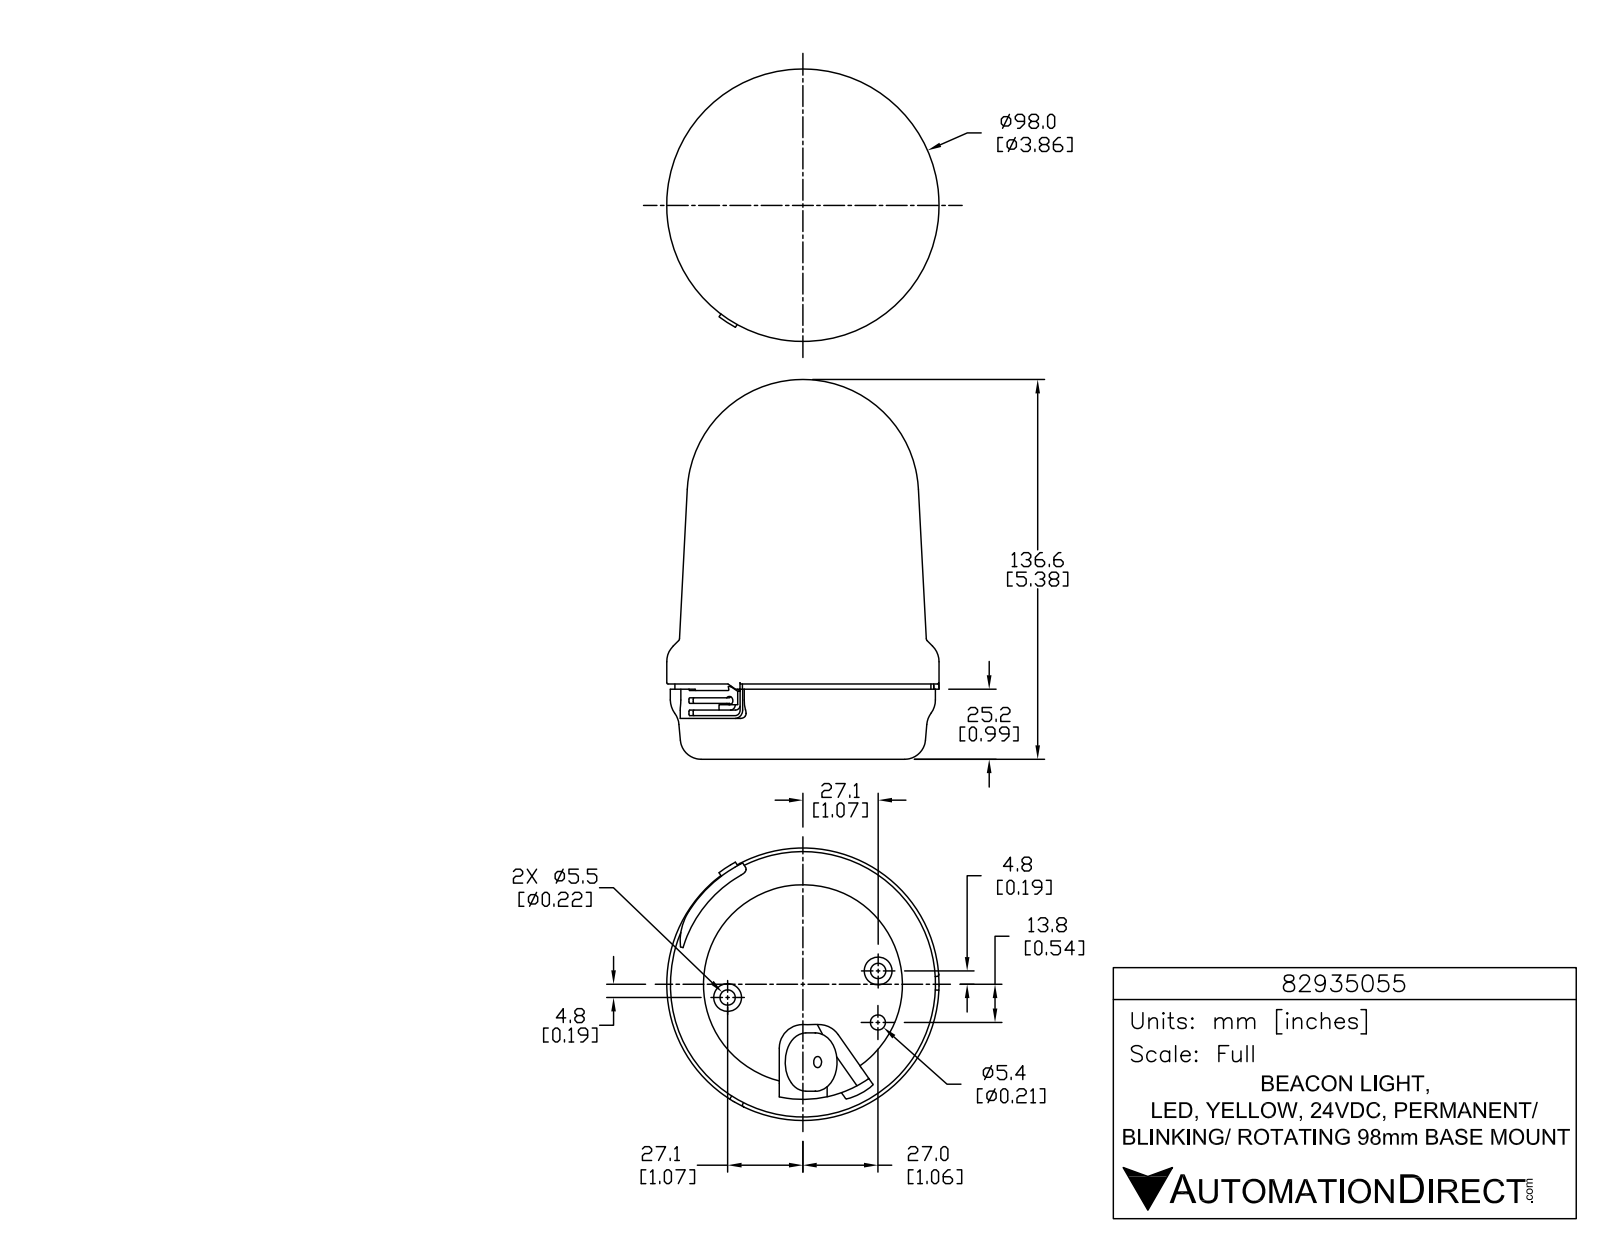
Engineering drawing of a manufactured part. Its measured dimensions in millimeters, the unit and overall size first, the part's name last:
Units: millimetres
Overall size (bounding box): 136.6 × 98 × 98
Round holes (diameter × count): ⌀1.5 ×3, ⌀5.5 ×2, ⌀4 ×1, ⌀5.4 ×1, ⌀71.6 ×1
Round bosses / shafts (diameter × count): ⌀8.6 ×3, ⌀2.1 ×3, ⌀10 ×2, ⌀98 ×1, ⌀95.4 ×1, ⌀92.1 ×1, ⌀21 ×1
Partial cylindrical surfaces — rounded edges, fillets, slot ends (radius × count): R0.1 ×9, R0.1 ×6, R0.3 ×6, R0.3 ×6, R0.3 ×6, R5 ×6, R0.5 ×5, R1 ×4
Main face-to-face distances: 26.5, 24.7, 1.9, 0.5, 25.2, 27.1, 6, 14.7, 14.2, 10.5
Hole centre spacings: 27.5, 18.5, 30.3, 54.8, 55
Volume: 732 300 mm³ · Surface area: 47 520 mm²
Bodies: 1 solid, 872 faces (566 planar, 204 cylindrical, 102 other)
Part name (STEP PRODUCT): 82935055
STEP written by: SolidWorks 2015 (AUTOMOTIVE_DESIGN)
